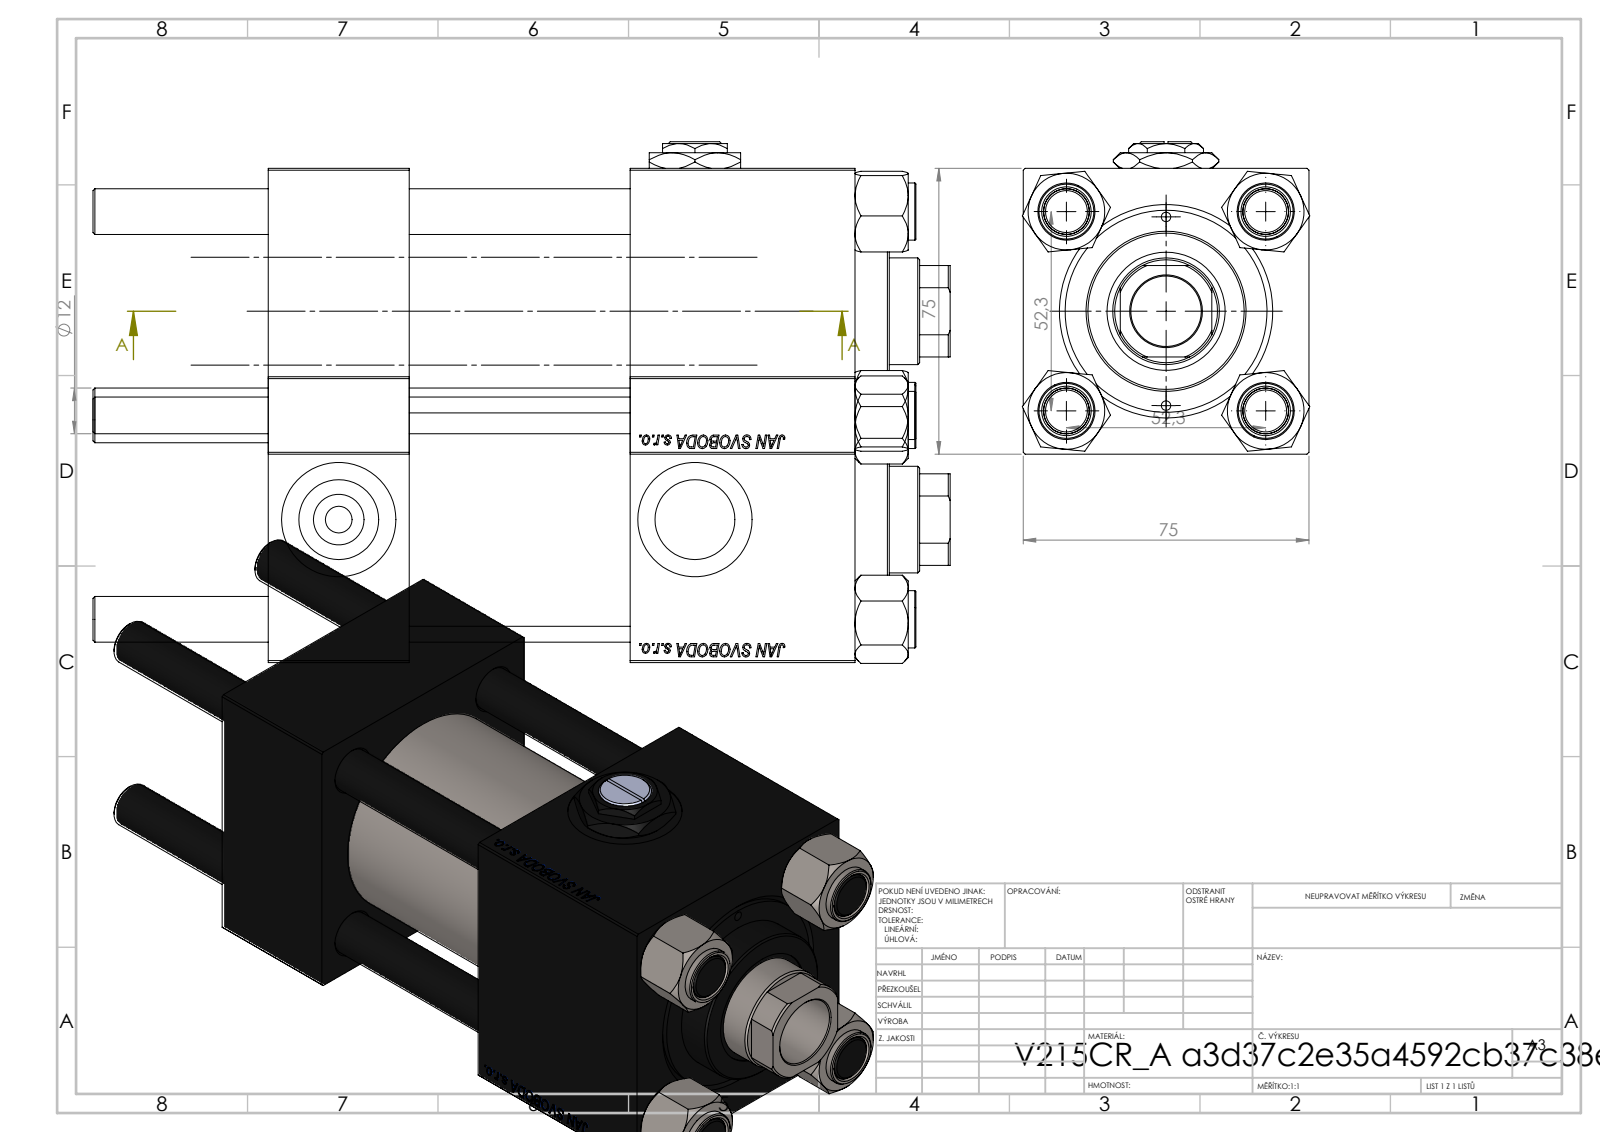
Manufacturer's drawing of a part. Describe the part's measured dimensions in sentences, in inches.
The part is named "V215_VC_A; V215CR_BODY_A; NUT_M5; Zatka_pro_OIL_PORT (+2 more)". Its 3-D file was written by "SolidWorks 2019 (CONFIG_CONTROL_DESIGN)". It is 12 solids with 1187 faces: 545 planar, 86 cylindrical and 556 other. Overall it measures 8.858 by 3.228 by 2.97 inches. Its volume is 42.64 cubic inches and its surface area 262.6 square inches. Round holes: 4 of diameter 0.472, 2 of diameter 0.098, 2 of diameter 0.276, 2 of diameter 0.825, 2 of diameter 1.181, 1 of diameter 0.728, 1 of diameter 1.102, 1 of diameter 1.22, 1 of diameter 1.614, 1 of diameter 1.969, 1 of diameter 2.087. Round bosses or shafts: 4 of diameter 0.591, 1 of diameter 2.205, 1 of diameter 1.654. Partial cylindrical surfaces (rounded edges, fillets, slot ends): 1 of radius 0.531. The main face-to-face distances are 2.953, 1.457, 6.063, 4.606, 3.74, 2.323, 2.283, 4.933, 3.476, 1.193. The hole center spacings are 1.031, 1.456, 2.059, 2.253, 0.974, 2.912, 1.949, 3.681.
